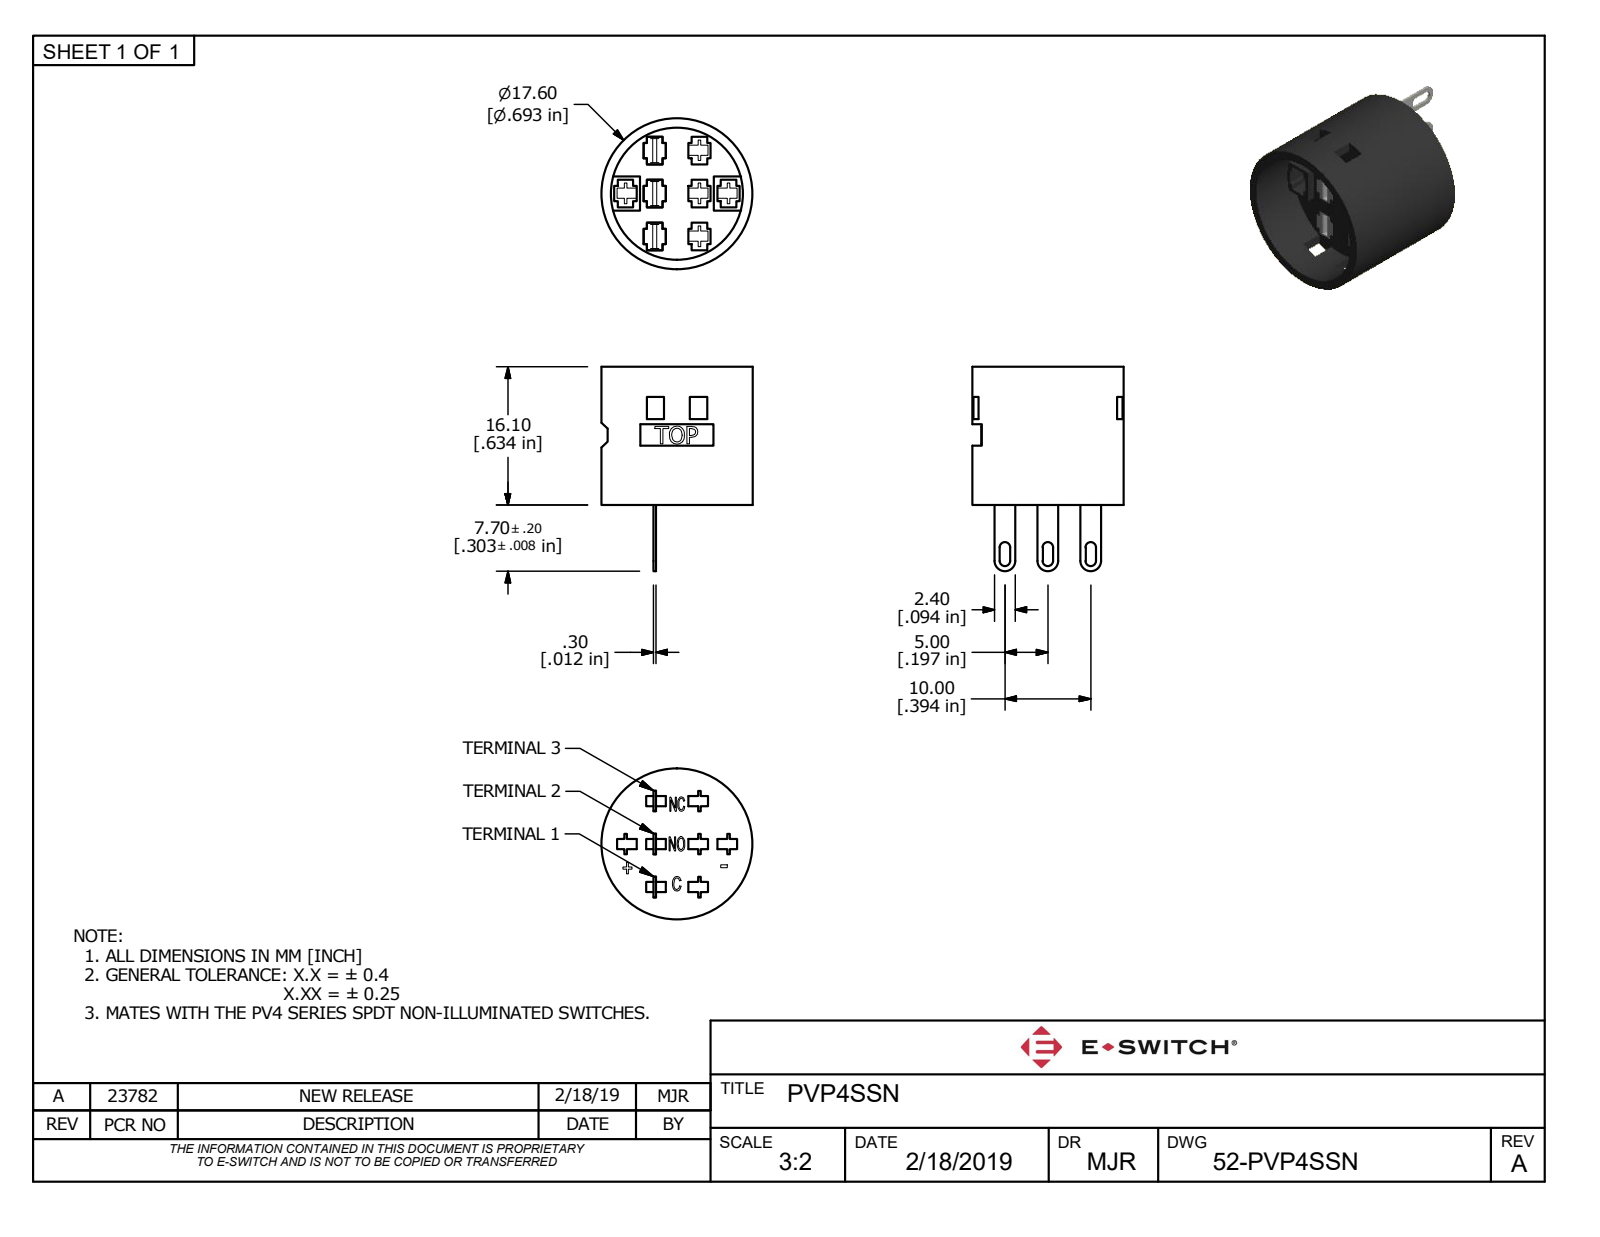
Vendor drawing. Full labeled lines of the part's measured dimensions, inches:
Part name (STEP PRODUCT): PVP4SSN
STEP written by: Autodesk Inventor 2018 (AP242_MANAGED_MODEL_BASED_3D_ENGINEERING_MIM_LF)
Units: inches
Bodies: 1 solid, 425 faces (359 planar, 17 cylindrical, 49 other)
Overall size (bounding box): 0.941 × 0.693 × 0.693
Volume: 0.142 in³ · Surface area: 4.081 in²
Round holes (diameter × count): ⌀0.606 ×1
Round bosses / shafts (diameter × count): ⌀0.693 ×1
Partial cylindrical surfaces — rounded edges, fillets, slot ends (radius × count): R0.024 ×6, R0.047 ×3, R0.01 ×2
Main face-to-face distances: 0.016, 0.071, 0.098, 0.087, 0.339, 0.39, 0.126, 0.197, 0.102, 0.134
